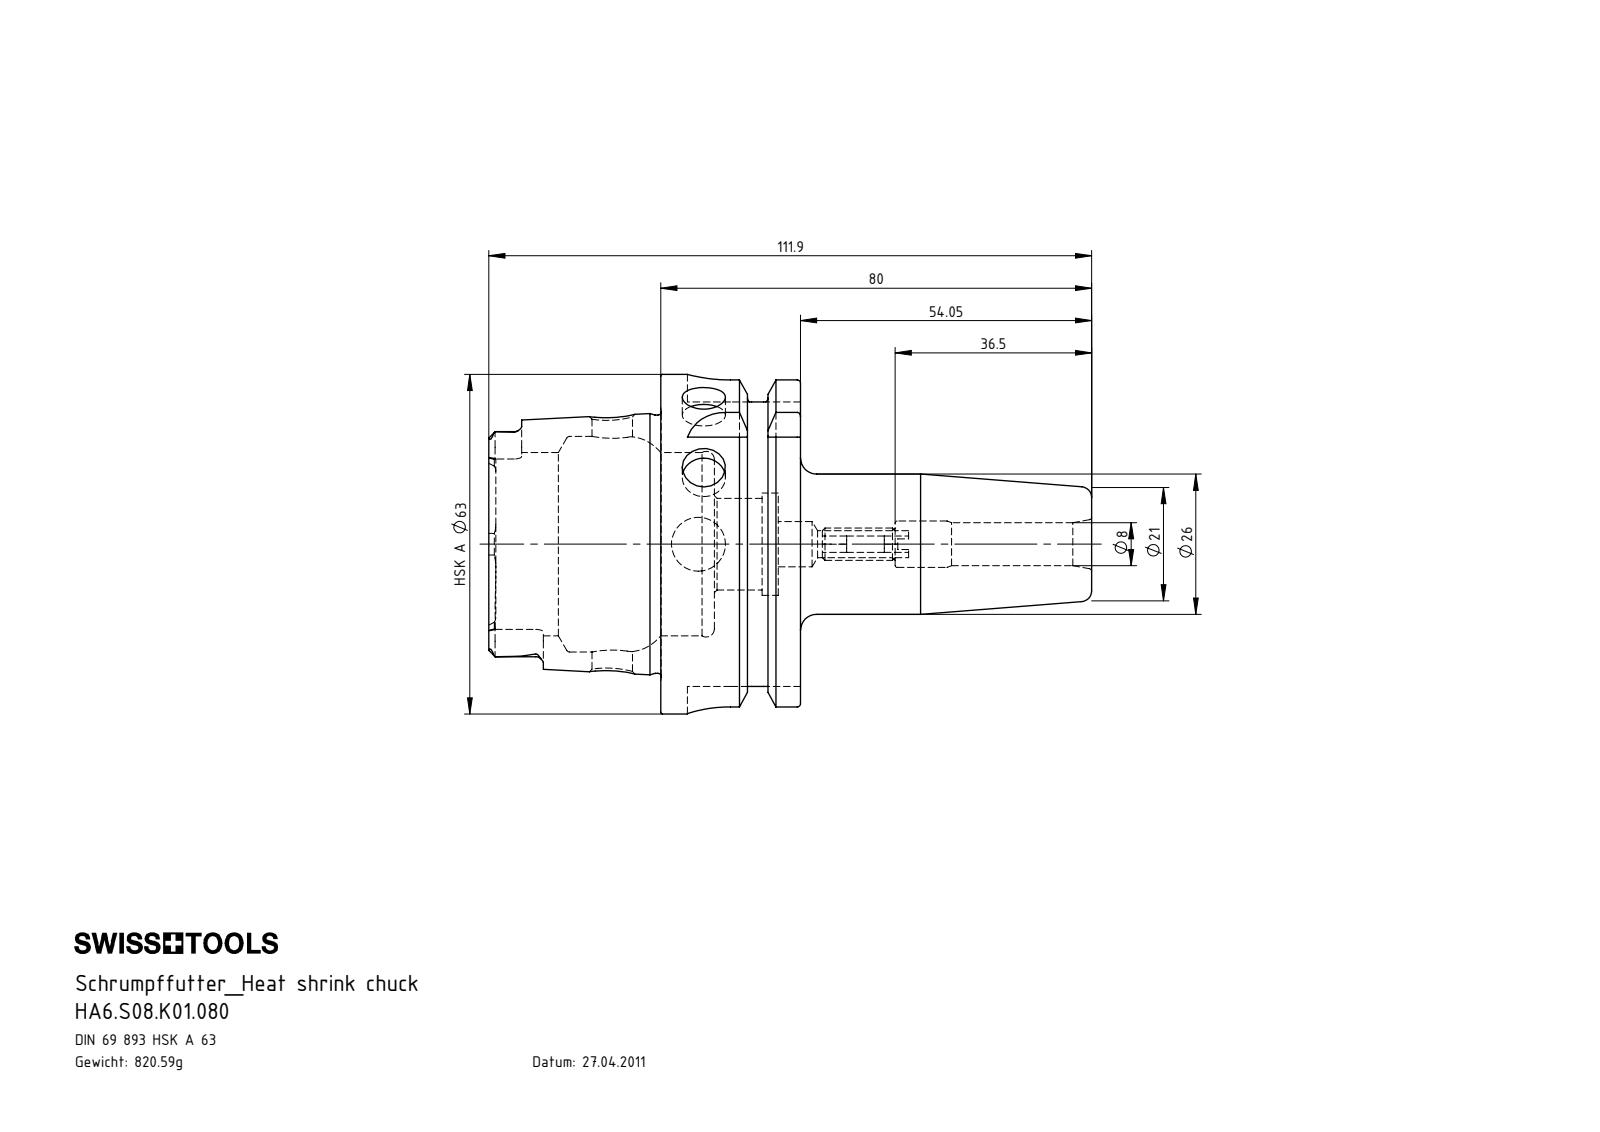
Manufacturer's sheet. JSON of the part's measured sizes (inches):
{"part_name": "HA6-S08.K01.080; ERU-AN2.K01.016_A; HA6-S08.K01.080_B_Fertigbearbeitung", "step_written_by": "SolidWorks 2012 (CONFIG_CONTROL_DESIGN)", "units": "inches", "bodies": {"solids": 2, "faces": 232, "planar": 82, "cylindrical": 61, "other": 89}, "overall_size": [4.406, 2.48, 2.48], "volume_in3": 6.379, "surface_area_in2": 43.41, "round_holes": [[0.315, 3], [0.118, 1], [0.197, 1], [0.295, 1], [0.331, 1], [0.339, 1], [0.394, 1], [0.669, 1], [0.748, 1], [1.339, 1], [1.575, 1]], "round_bosses_or_shafts": [[2.48, 1], [2.163, 1], [1.887, 1], [1.024, 1], [0.236, 1]], "partial_cylinders_radius": [[0.055, 6], [0.113, 4], [0.315, 4]], "face_to_face_distances": [1.022, 0.63, 0.392, 1.256, 1.648, 2.278, 2.079, 0.858, 0.467, 2.114]}
